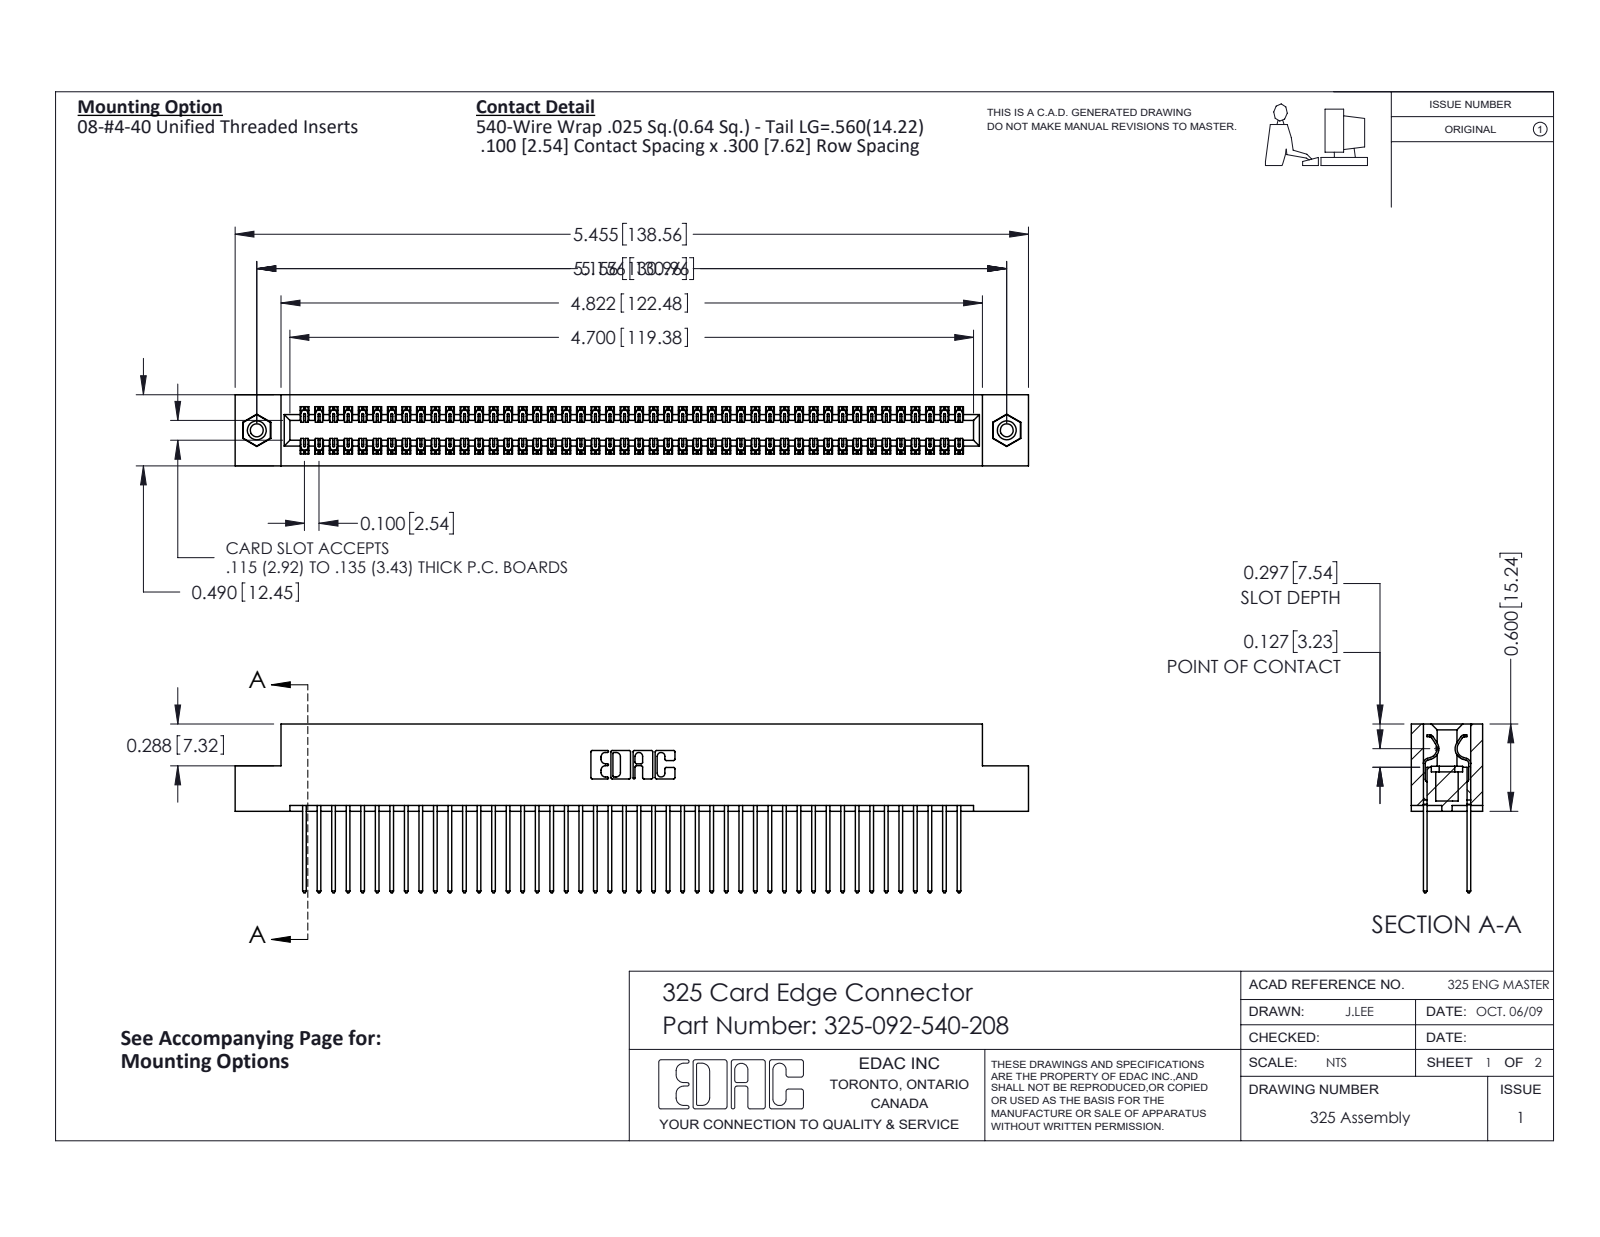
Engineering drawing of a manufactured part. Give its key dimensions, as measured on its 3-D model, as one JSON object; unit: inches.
{"part_name": "325 Part_TI; 345-250-001_345-250-003-102; 325-292-001_325-293-140; 325-092-540-208", "step_written_by": "SolidWorks 2016 (CONFIG_CONTROL_DESIGN)", "units": "inches", "bodies": {"solids": 95, "faces": 4958, "planar": 3414, "cylindrical": 1528, "other": 16}, "overall_size": [5.455, 1.16, 0.49], "volume_in3": 1.115, "surface_area_in2": 37.01, "round_holes": [[0.089, 2], [0.125, 2], [0.16, 2]], "round_bosses_or_shafts": [[0.155, 2]], "partial_cylinders_radius": [[0.006, 138], [0.01, 92], [0.01, 22], [0.007, 6], [0.031, 6], [0.026, 3], [0.014, 2], [0.022, 2]], "face_to_face_distances": [0.083, 0.407, 0.3, 0.107, 0.383, 0.025, 0.325, 0.49, 0.275, 0.56], "hole_center_spacings": [5.156]}
